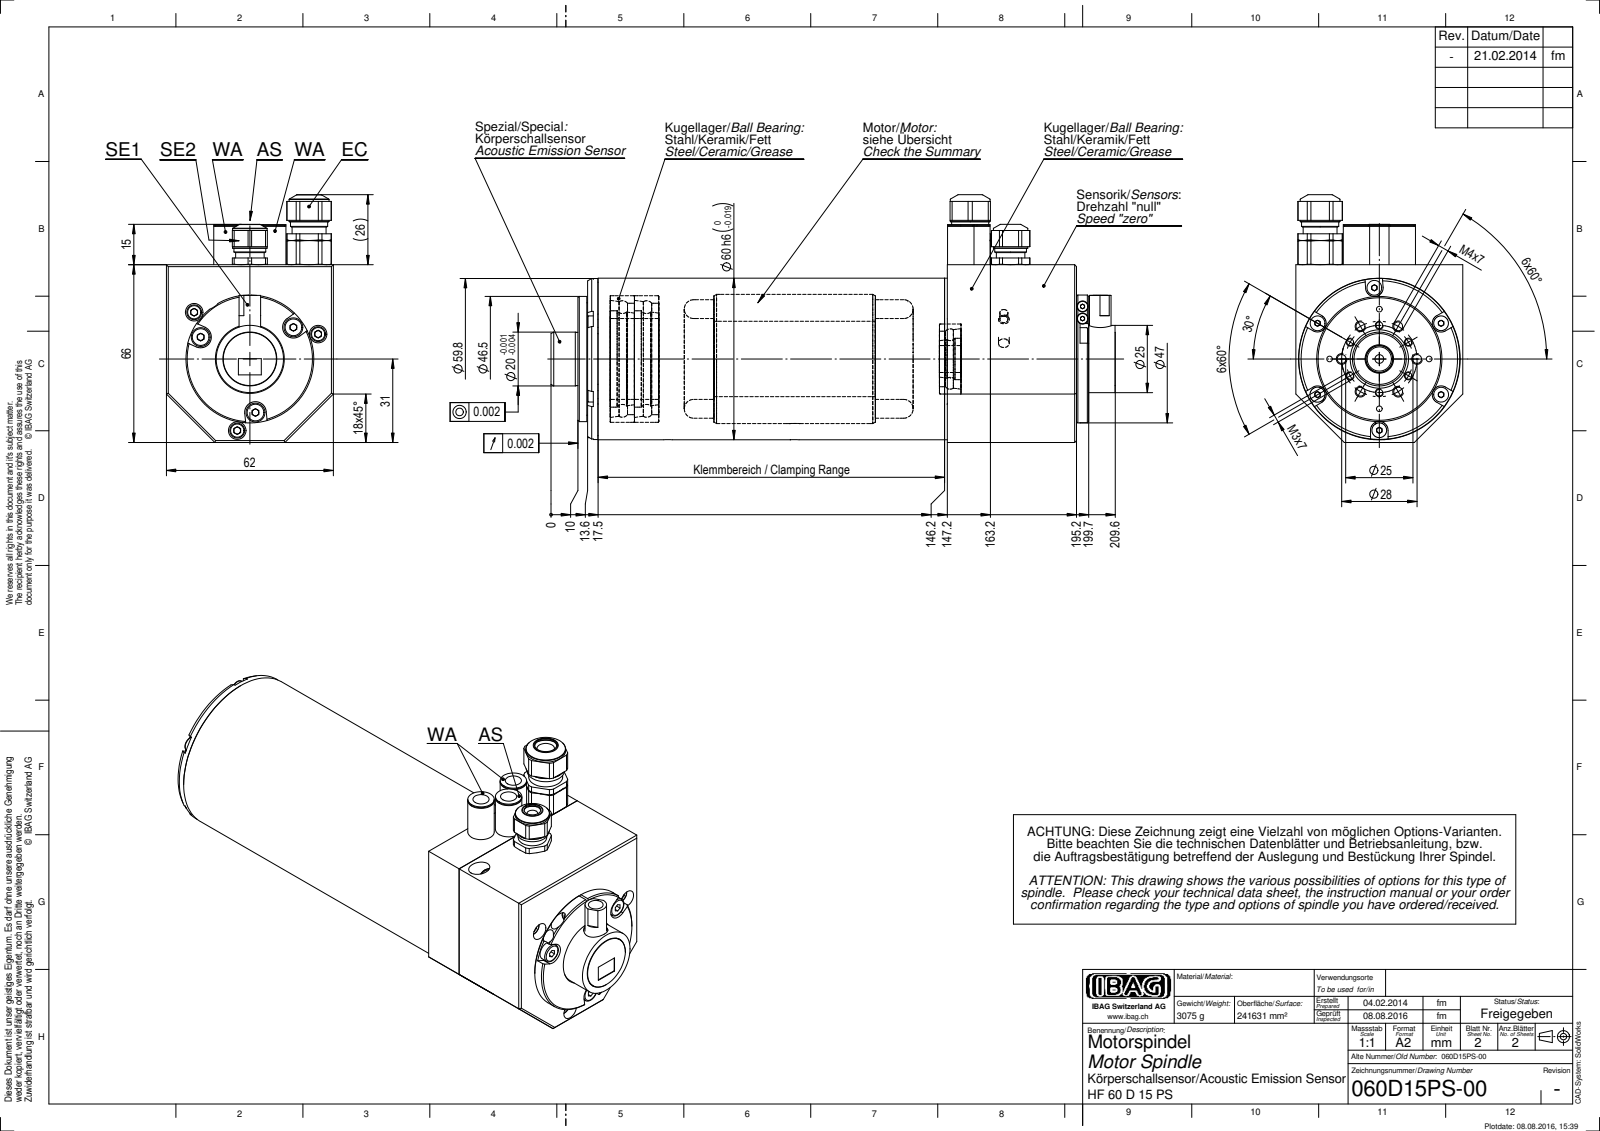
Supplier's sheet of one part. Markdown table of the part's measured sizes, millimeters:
| quantity | value |
| --- | --- |
| part name | 060D15PS-00 |
| STEP written by | SolidWorks 2014 (CONFIG_CONTROL_DESIGN) |
| units | millimeters |
| bodies | 0 solids, 474 faces (195 planar, 181 cylindrical, 98 other) |
| overall size | 209.6 × 92 × 62 |
| round holes (diameter × count) | 3.3 × 8, 2.5 × 6, 2.1 × 4, 6.5 × 4, 6 × 3, 8 × 3, 4.1 × 2, 7 × 2, 3.24 × 1, 4 × 1, 5.5 × 1, 6.2 × 1 |
| round bosses / shafts (diameter × count) | 5.5 × 6, 9.8 × 3, 60 × 1, 59.8 × 1, 50 × 1, 46.5 × 1, 25 × 1, 20 × 1 |
| partial cylindrical surfaces (radius × count) | 3.25 × 6, 7.15 × 1, 8.25 × 1 |
| main face-to-face distances | 62, 66, 4.5, 185.2, 189.7, 3.6, 181.6, 186.1, 137.2, 133.6 |
| hole center spacings | 12.5, 7.01, 14, 18.77, 25.6, 25.58, 32.5, 9.47 |
